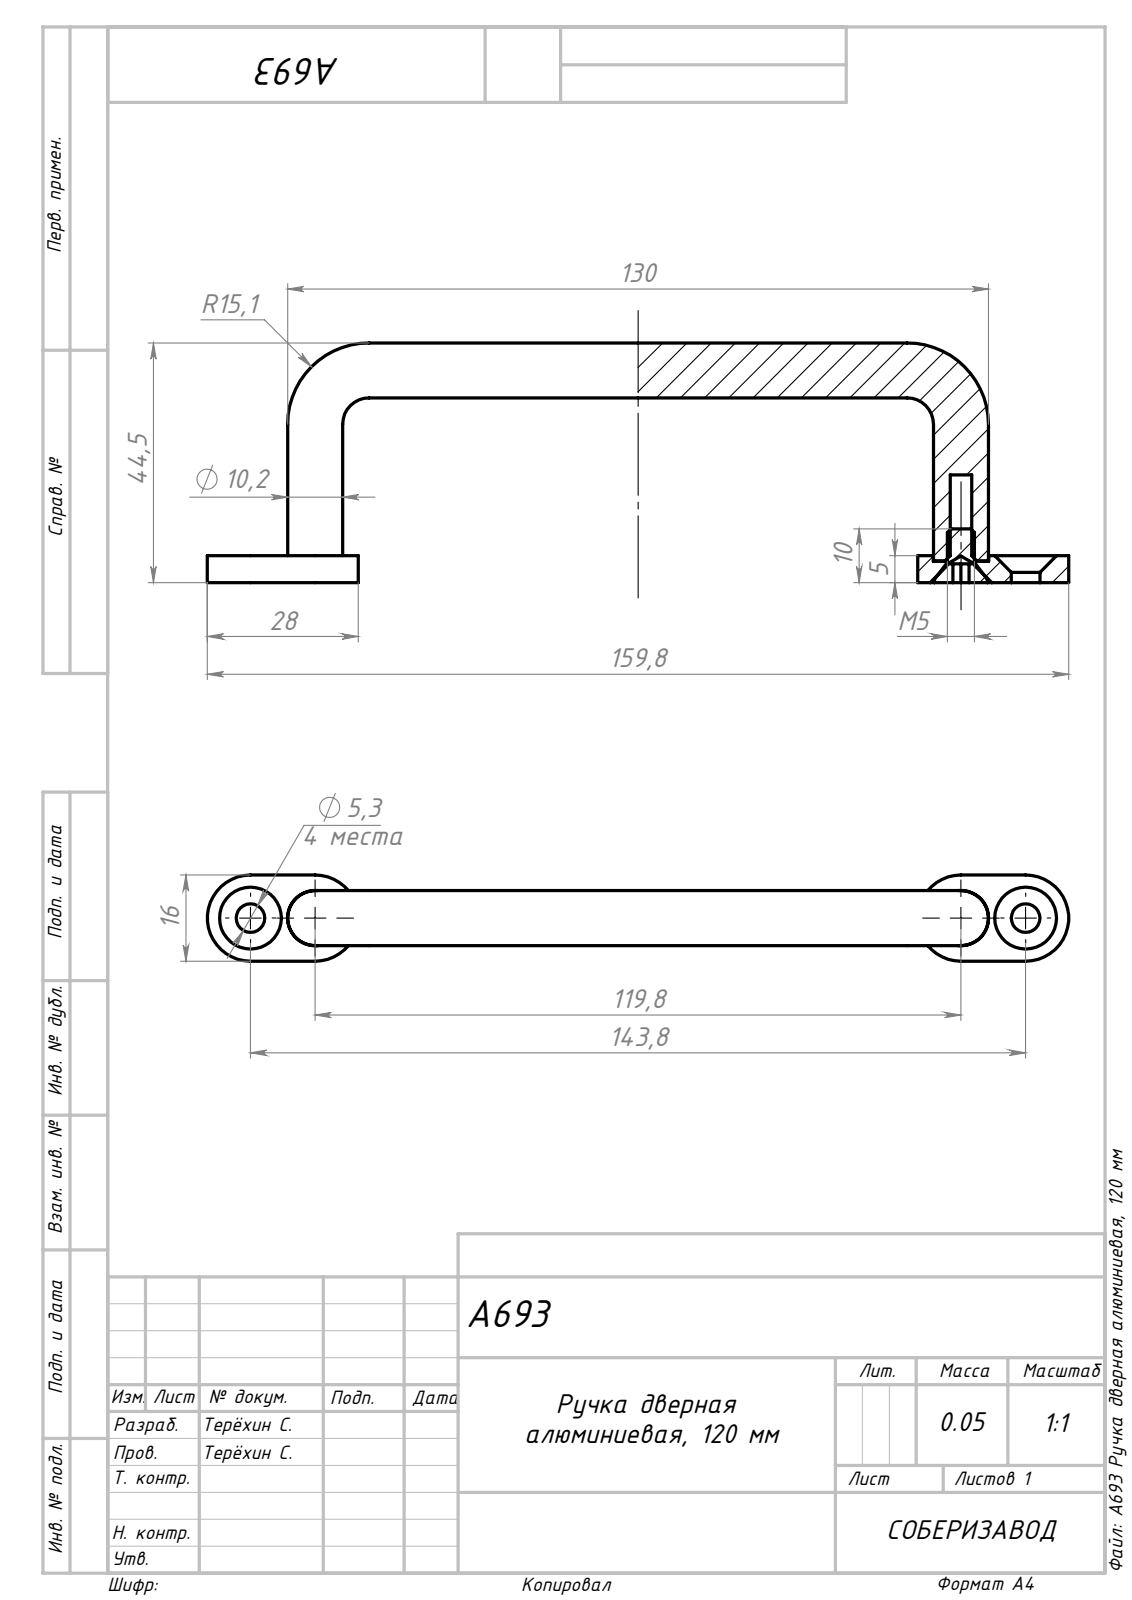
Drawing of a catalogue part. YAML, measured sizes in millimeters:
part_name: "A693 Ручка_00; A693 Крепление ручки_00; A693 Ручка дверная алюминиевая, 120 мм; Винт M5x10 DIN 7991_00"
step_written_by: "SolidWorks 2022 (AUTOMOTIVE_DESIGN)"
units: millimeters
bodies: {solids: 5, faces: 100, planar: 32, cylindrical: 36, other: 32}
overall_size: [159.8, 44.5, 16]
volume: 17923
surface_area: 9538
round_holes:
  - {diameter: 5.3, count: 4}
  - {diameter: 4, count: 2}
  - {diameter: 10.25, count: 2}
round_bosses_or_shafts:
  - {diameter: 10.2, count: 3}
  - {diameter: 9.8, count: 2}
  - {diameter: 5, count: 2}
partial_cylinders:
  - {radius: 8, count: 4}
face_to_face_distances: [5, 4, 1, 16, 10, 3, 20, 15, 59.9, 3.5]
hole_center_spacings: [12, 131.8, 119.8, 143.8]
